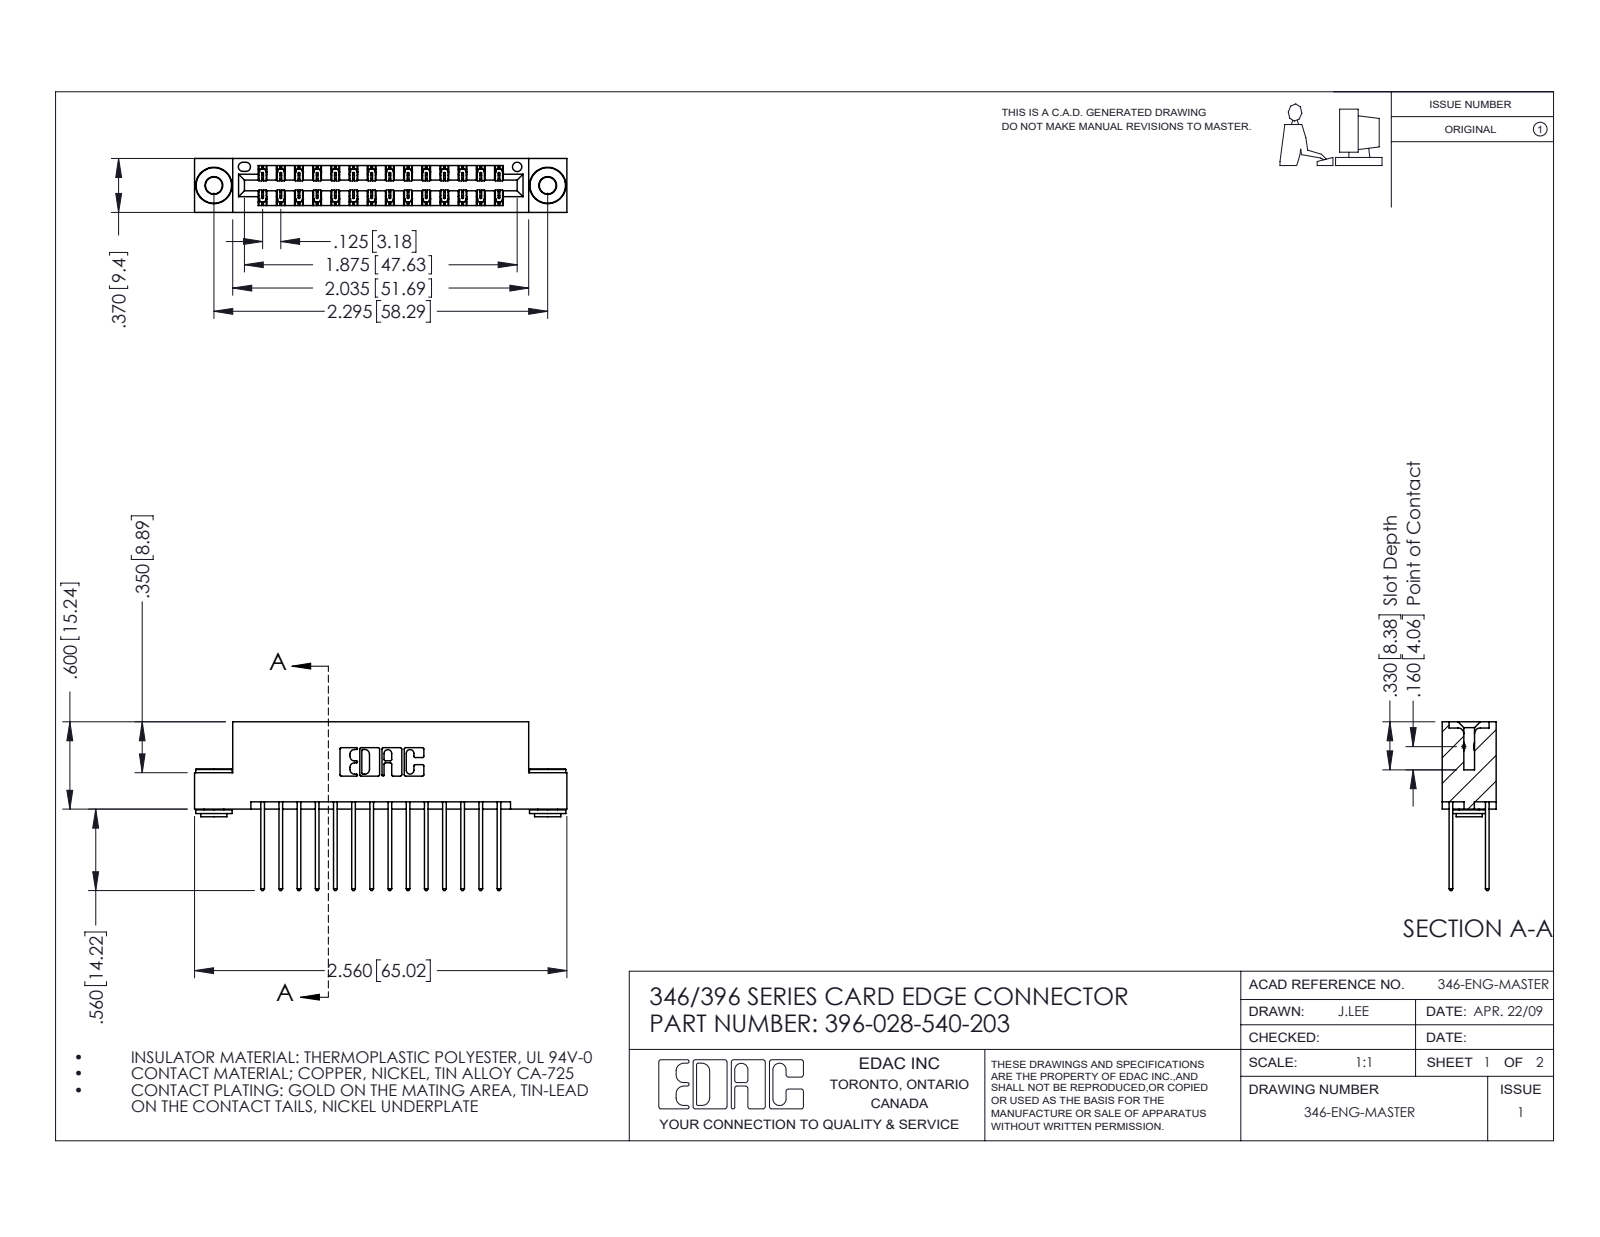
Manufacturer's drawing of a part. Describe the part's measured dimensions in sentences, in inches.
The part is named "396-028-540-203; 345-250-002_345-250-002-102; 346 Part_Flush Mounting Lugs - 0.156 Dia-TH; 345-292-001_345-293-140". Its 3-D file was written by "SolidWorks 2016 (CONFIG_CONTROL_DESIGN)". It is 31 solids with 1616 faces: 1066 planar, 542 cylindrical and 8 other. Overall it measures 2.56 by 1.16 by 0.37 inches. Its volume is 0.381 cubic inches and its surface area 13.74 square inches. Round holes: 2 of diameter 0.116, 2 of diameter 0.156, 1 of diameter 0.064. Round bosses or shafts: 2 of diameter 0.25, 2 of diameter 0.18, 2 of diameter 0.136. Partial cylindrical surfaces (rounded edges, fillets, slot ends): 42 of radius 0.006, 28 of radius 0.01, 22 of radius 0.01, 6 of radius 0.007, 6 of radius 0.031, 3 of radius 0.026, 2 of radius 0.014, 2 of radius 0.022. The main face-to-face distances are 0.25, 0.048, 0.322, 0.37, 0.025, 0.072, 0.298, 0.275, 0.148, 0.222. The hole center spacings are 0.246, 2.089, 2.295.
